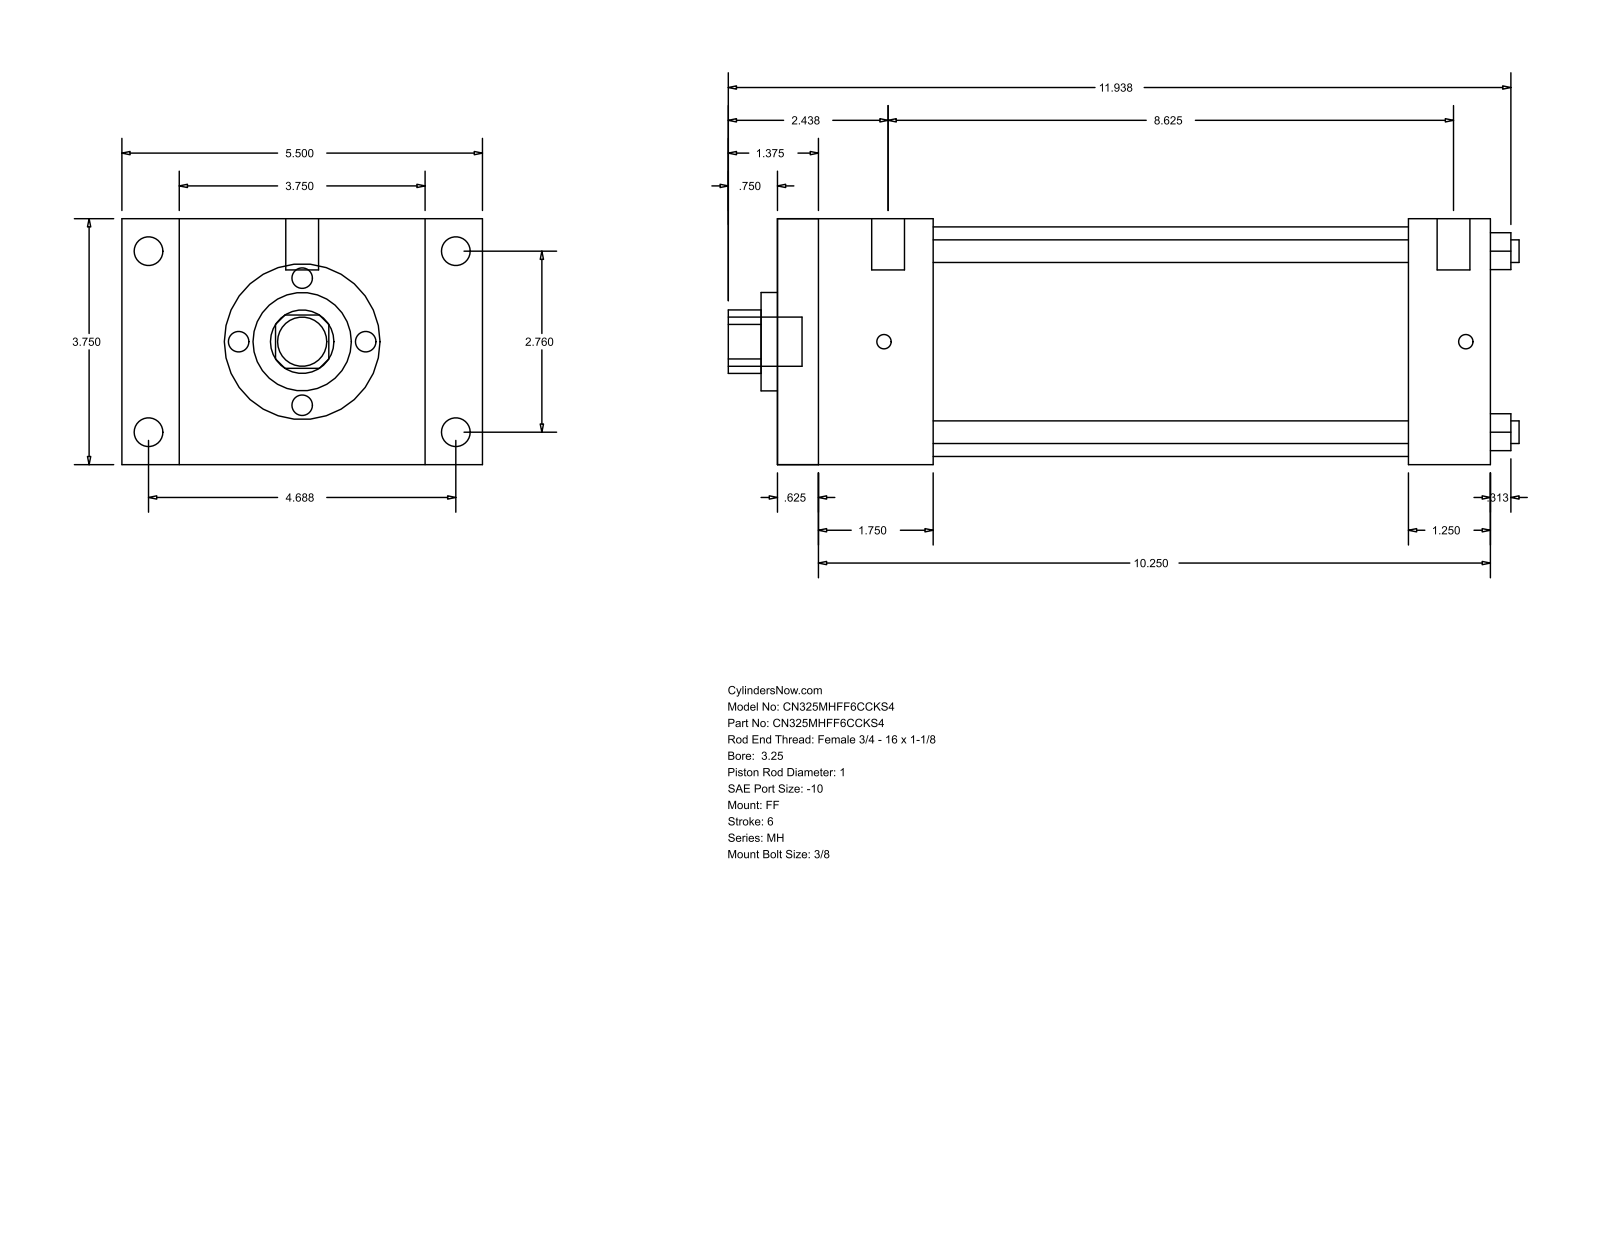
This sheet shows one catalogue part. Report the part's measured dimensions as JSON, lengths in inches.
{"part_name": "MH_FF__0325_1", "step_written_by": "GSSL Pune (CONFIG_CONTROL_DESIGN)", "units": "inches", "bodies": {"solids": 0, "faces": 92, "planar": 64, "cylindrical": 28, "other": 0}, "overall_size": [12.063, 5.5, 3.75], "round_holes": [[0.345, 4], [1, 1], [1.5, 1], [3.5, 1]], "round_bosses_or_shafts": [[0.438, 4], [0.219, 4], [0.5, 2], [0.75, 1]], "partial_cylinders_radius": [[0.484, 1]], "face_to_face_distances": [3.75, 10.875, 0.625, 10.25, 0.875, 4.625, 9.625, 9, 1.25, 2.375], "hole_center_spacings": [1.952, 2.76, 3.903]}
